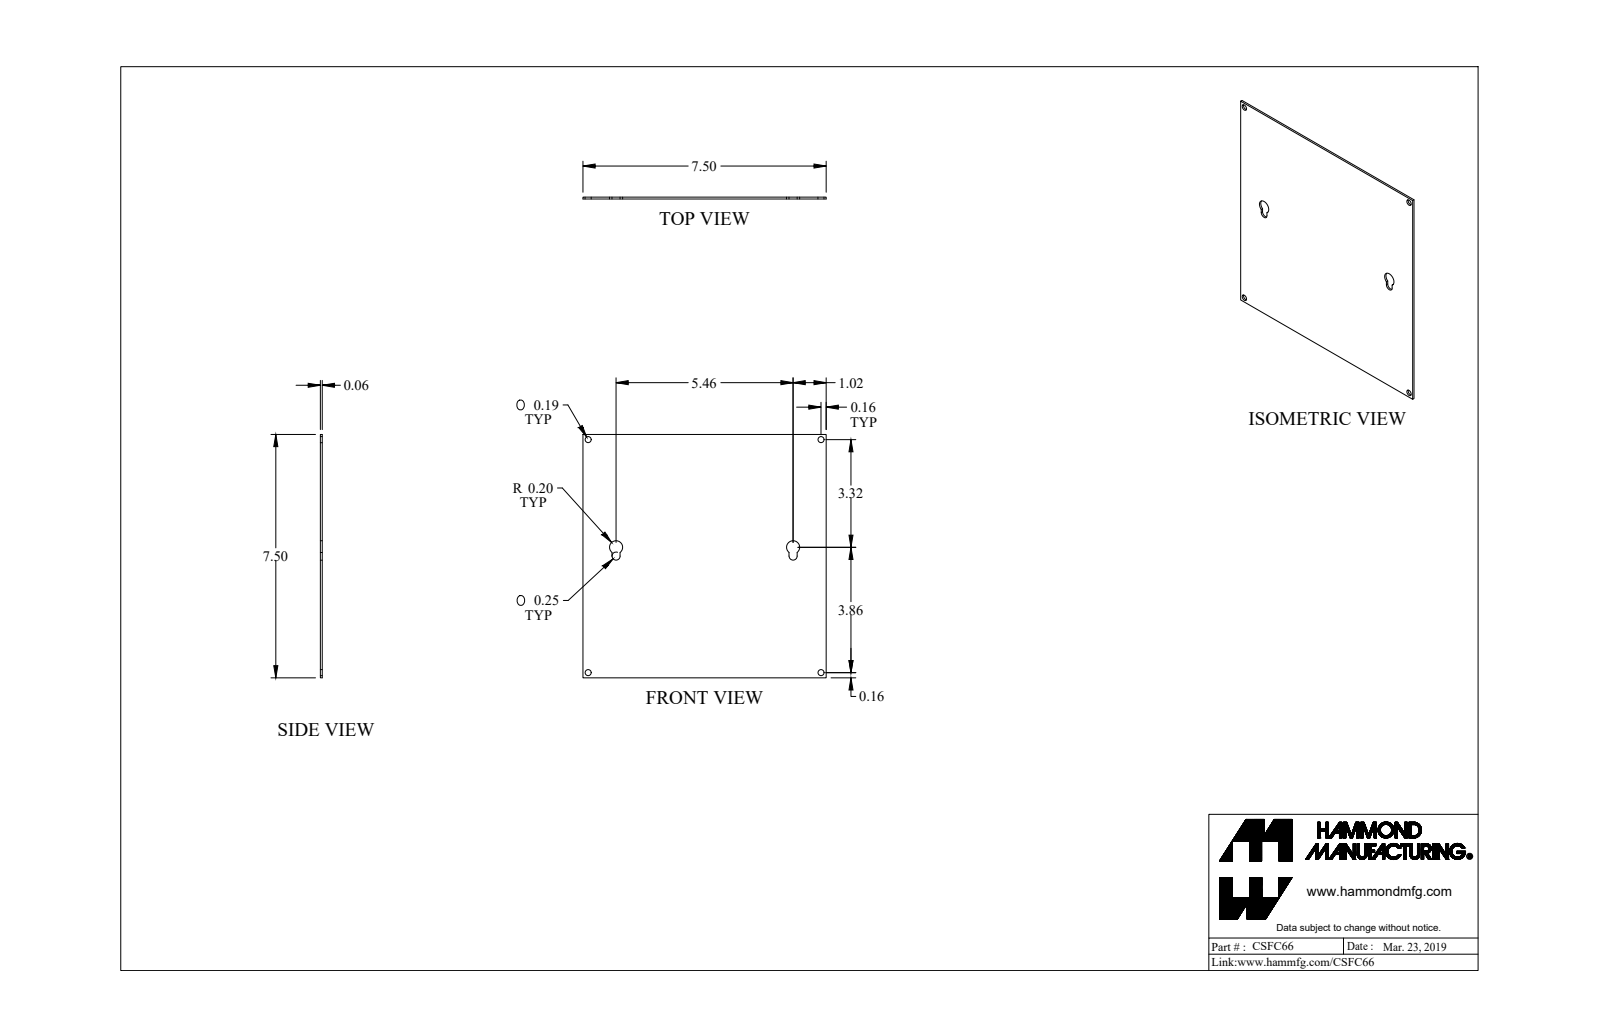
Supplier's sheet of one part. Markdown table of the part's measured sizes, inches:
| quantity | value |
| --- | --- |
| part name | CSFC66_Default |
| STEP written by | SolidWorks 2019 (CONFIG_CONTROL_DESIGN) |
| units | inches |
| bodies | 1 solid, 26 faces (10 planar, 16 cylindrical, 0 other) |
| overall size | 7.5 × 7.5 × 0.057 |
| volume | 3.18 in³ |
| surface area | 113.6 in² |
| round holes (diameter × count) | 0.188 × 4 |
| partial cylindrical surfaces (radius × count) | 0.125 × 2, 0.203 × 2 |
| main face-to-face distances | 0.057, 7.5, 0.895, 1.145, 6.355, 6.605, 5.46, 0.25, 5.71, 5.21 |
| hole center spacings | 7.18, 10.154 |
